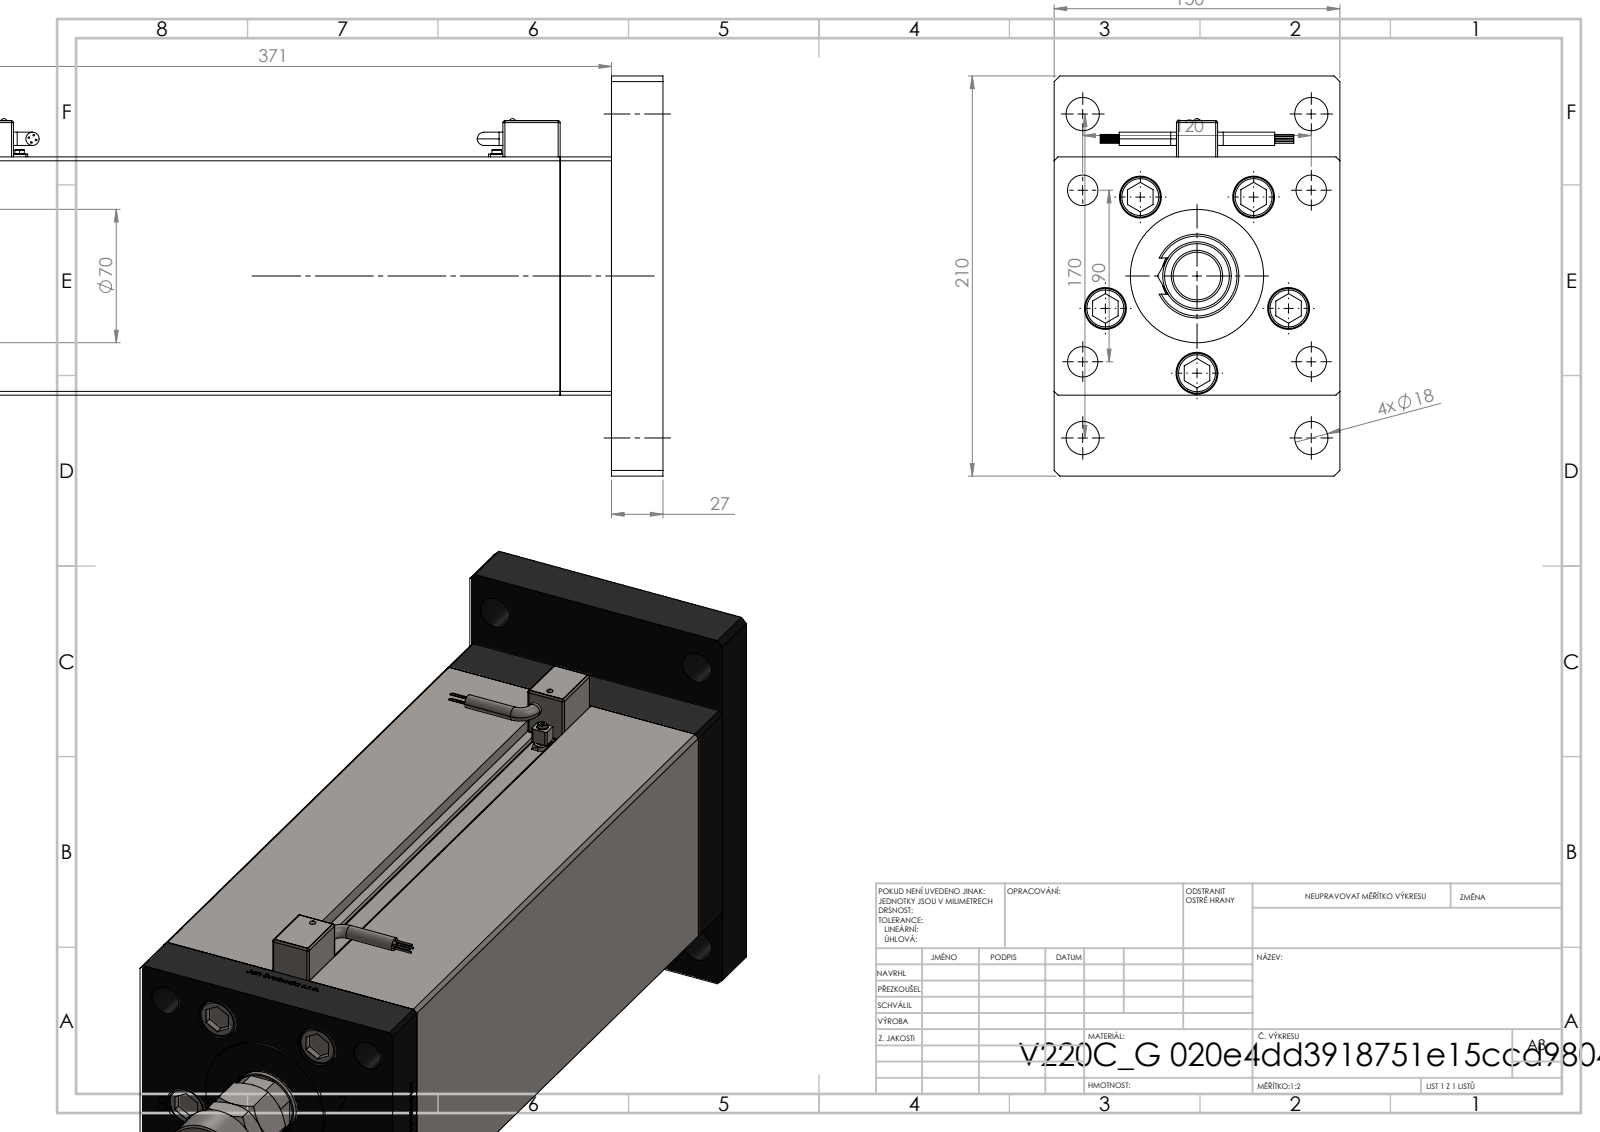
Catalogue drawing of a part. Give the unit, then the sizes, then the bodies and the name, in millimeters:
Units: millimetres
Overall size (bounding box): 523.5 × 210 × 150
Round holes (diameter × count): ⌀16 ×9, ⌀17.5 ×9, ⌀22 ×5, ⌀21 ×4, ⌀2 ×2, ⌀3.6 ×2, ⌀5 ×2, ⌀7 ×2, ⌀13.16 ×2, ⌀25.5 ×1, ⌀36 ×1, ⌀37.5 ×1
Round bosses / shafts (diameter × count): ⌀8 ×9, ⌀0.85 ×8, ⌀21 ×5, ⌀7 ×4, ⌀6 ×2, ⌀3.5 ×2, ⌀2.5 ×2, ⌀80 ×1
Partial cylindrical surfaces — rounded edges, fillets, slot ends (radius × count): R1 ×24, R4 ×4, R0.93 ×2, R9.5 ×1, R15 ×1, R17.5 ×1
Main face-to-face distances: 27, 150, 125, 344, 371, 317, 54, 2, 398, 6.5
Hole centre spacings: 51, 40, 75, 104.04, 120, 126.49, 130, 176.92
Volume: 6 653 000 mm³ · Surface area: 640 564 mm²
Bodies: 23 solids, 1602 faces (624 planar, 292 cylindrical, 686 other)
Part name (STEP PRODUCT): MFA; V220C_F; V220C_G_MIDDLE; V220C BACK_G (+5 more)
STEP written by: SolidWorks 2019 (CONFIG_CONTROL_DESIGN)
